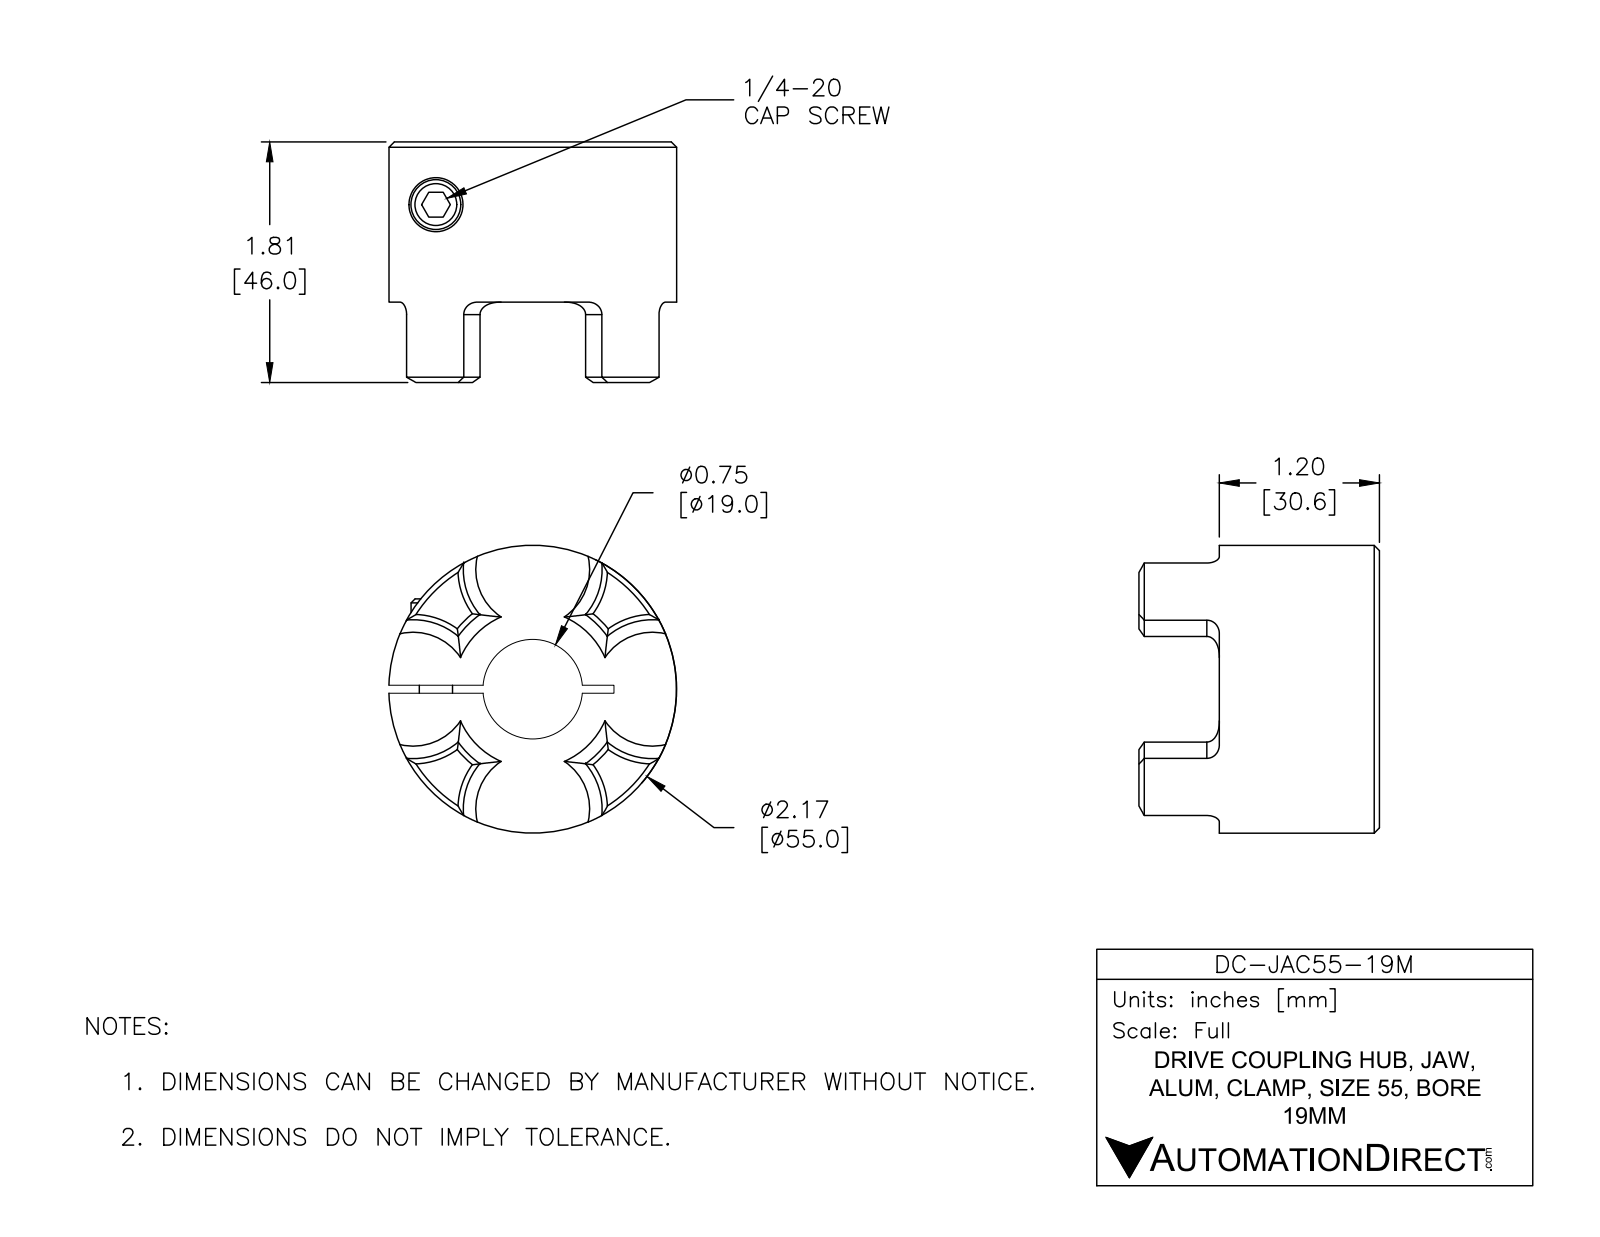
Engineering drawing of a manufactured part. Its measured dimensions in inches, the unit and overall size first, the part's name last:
Units: inches
Overall size (bounding box): 2.19 × 2.165 × 1.81
Round holes (diameter × count): ⌀0.266 ×1, ⌀0.406 ×1, ⌀0.748 ×1
Round bosses / shafts (diameter × count): ⌀2.165 ×1, ⌀0.375 ×1, ⌀0.25 ×1
Partial cylindrical surfaces — rounded edges, fillets, slot ends (radius × count): R0.522 ×4, R0.687 ×1
Main face-to-face distances: 1.205, 0.06, 1.81, 0.605, 0.46, 0.4, 0.187, 0.29, 0.35, 0.75
Volume: 4.133 in³ · Surface area: 25.41 in²
Bodies: 2 solids, 92 faces (22 planar, 29 cylindrical, 41 other)
Part name (STEP PRODUCT): DC-JA55-19M_POST2016
STEP written by: SolidWorks 2016 (AUTOMOTIVE_DESIGN)
